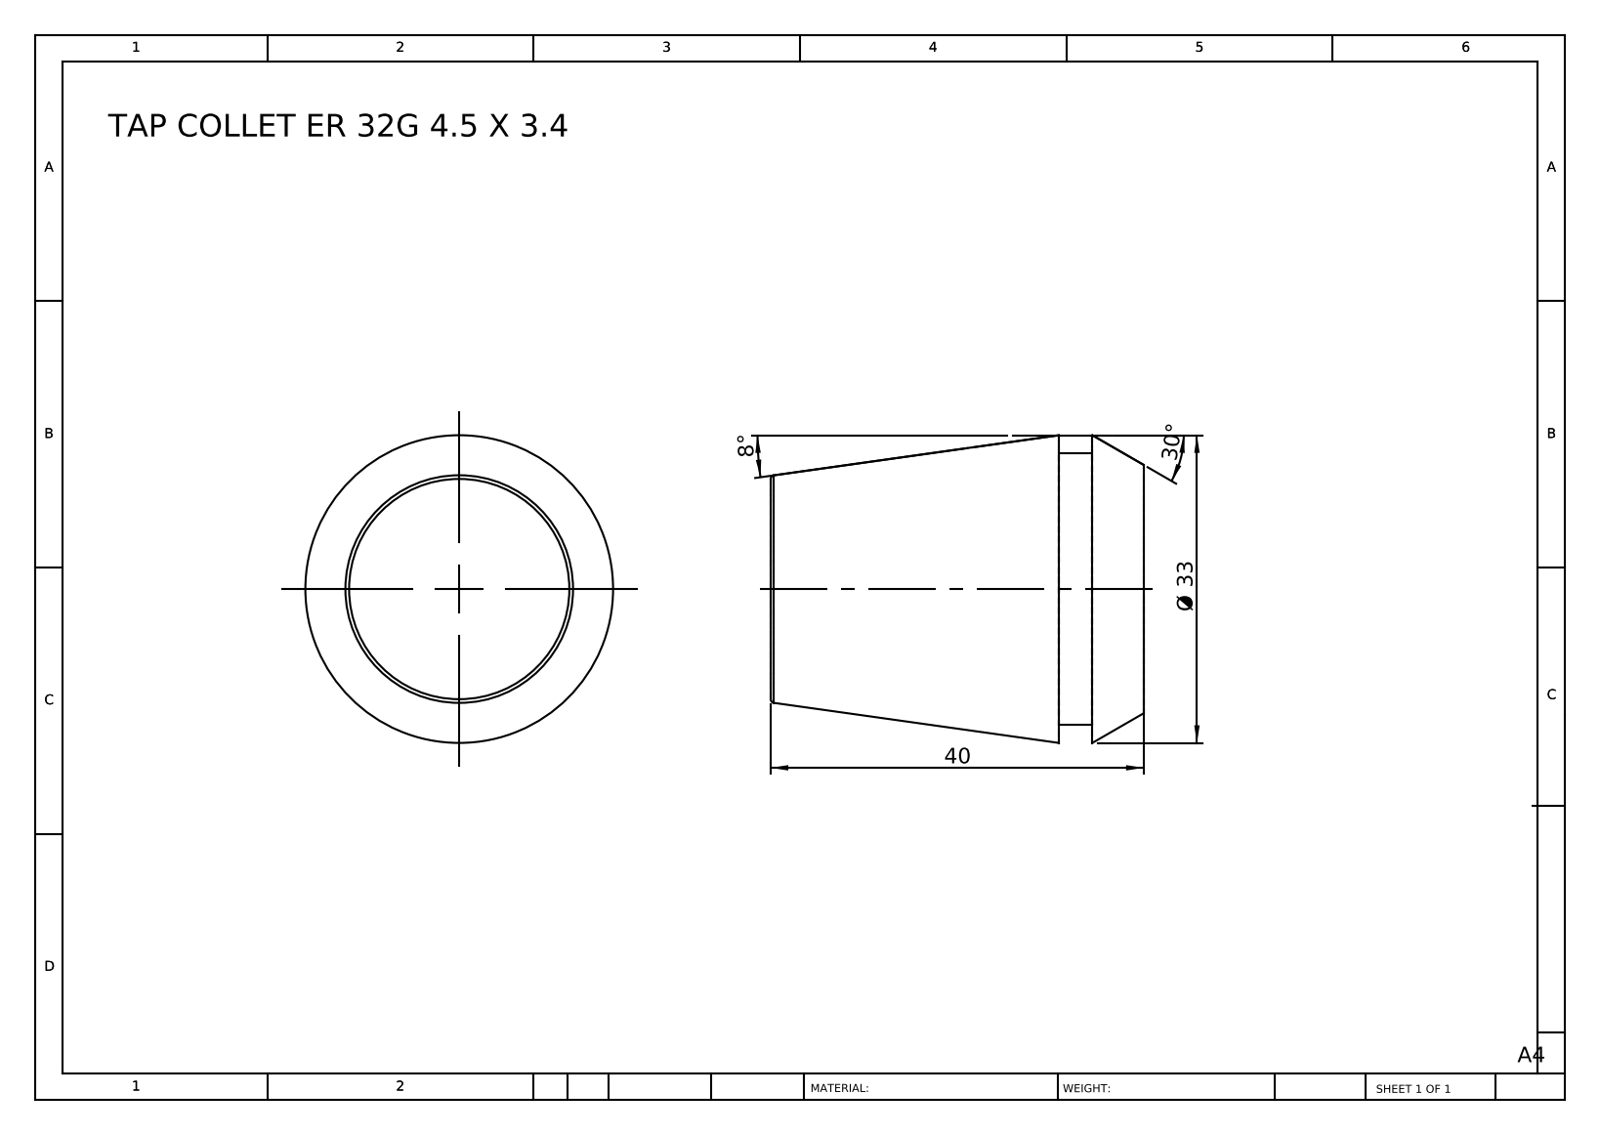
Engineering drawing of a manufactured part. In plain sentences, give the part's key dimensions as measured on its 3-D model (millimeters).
The part is named "TAP COLLET ER 32G 4.5 X 3.4". Its 3-D file was written by "SolidWorks 2014 (CONFIG_CONTROL_DESIGN)". It is 1 solid with 12 faces: 4 planar, 2 cylindrical and 6 other. Overall it measures 40 by 33 by 33 millimeters. Its volume is 26 350 cubic millimeters and its surface area 5 119 square millimeters. Round bosses or shafts: 1 of diameter 29.2. The main face-to-face distances are 40, 9.1, 30.9, 5.5, 3.6, 34.5.
